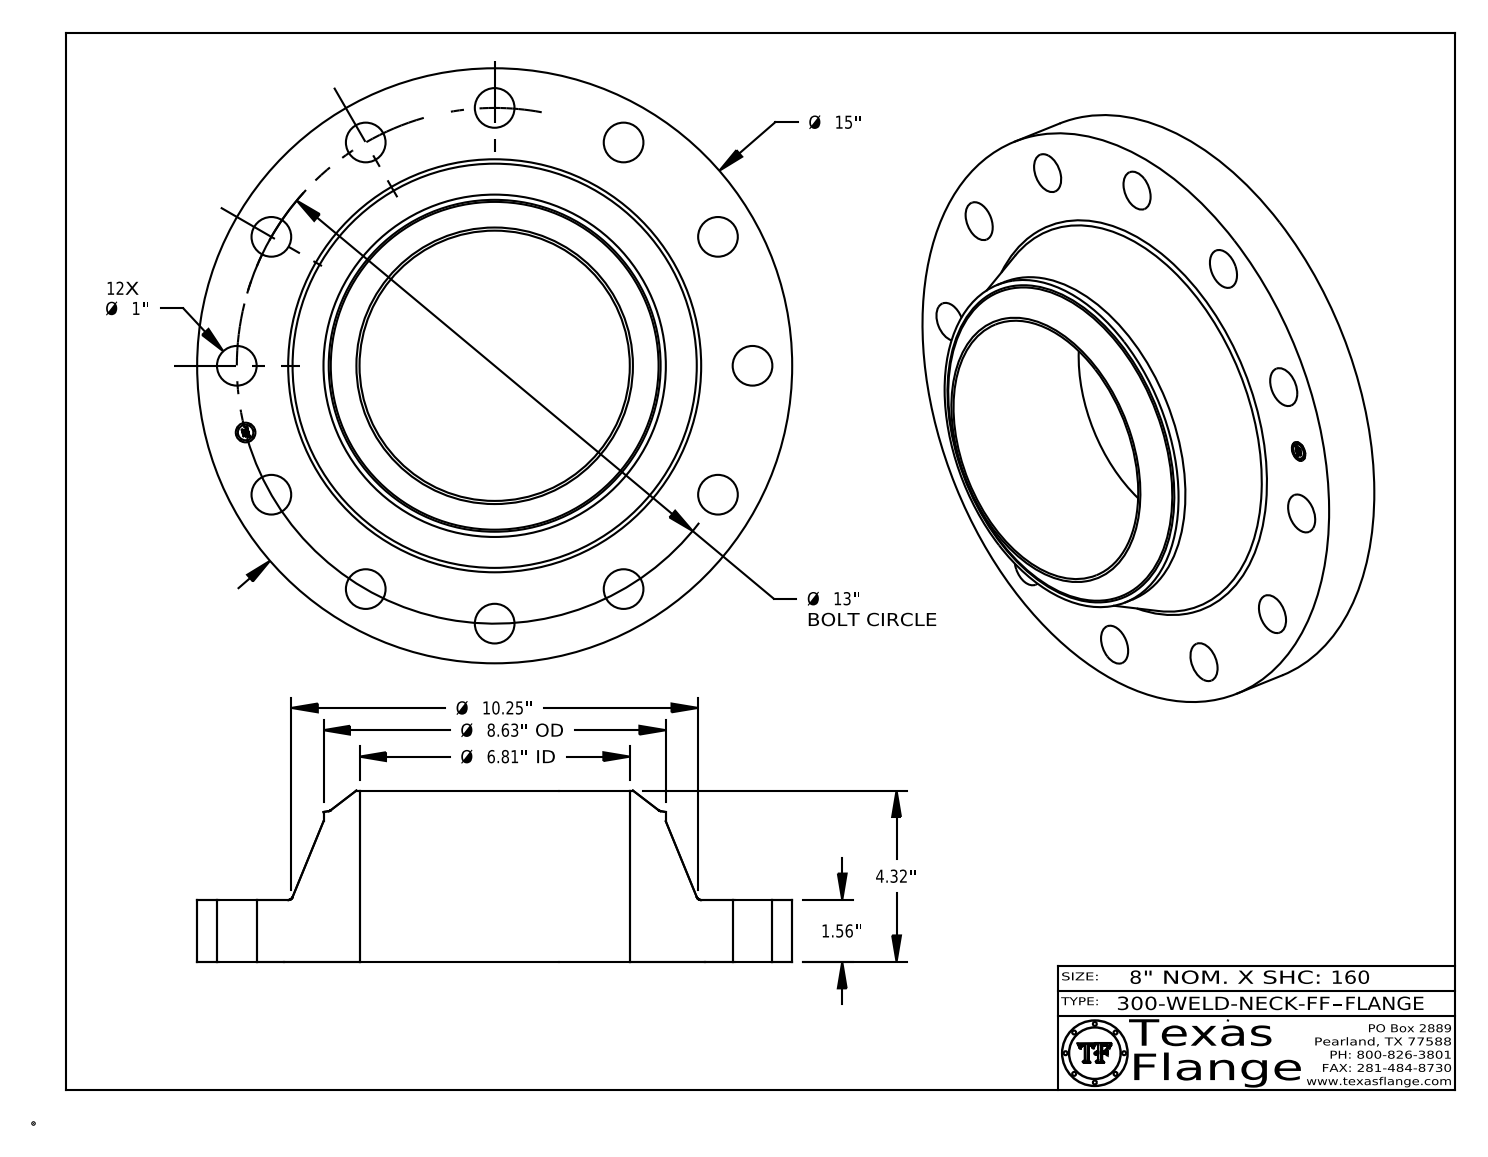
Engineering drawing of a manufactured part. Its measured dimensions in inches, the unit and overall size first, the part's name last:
Units: inches
Overall size (bounding box): 15 × 15 × 4.32
Round holes (diameter × count): ⌀1 ×12, ⌀0.495 ×1, ⌀6.813 ×1
Round bosses / shafts (diameter × count): ⌀0.03 ×8, ⌀15 ×1, ⌀8.63 ×1, ⌀0.39 ×1
Main face-to-face distances: 1.56, 4.32, 2.76, 1.545, 0.015, 2.775, 0.148, 0.144, 0.027, 0.096
Hole centre spacings: 6.5, 3.365, 9.193, 11.258, 12.557, 13, 1.697, 4.975
Volume: 281.6 in³ · Surface area: 536 in²
Bodies: 1 solid, 429 faces (369 planar, 50 cylindrical, 10 other)
Part name (STEP PRODUCT): 300-WELD-NECK-FF
STEP written by: CATIA V5 STEP AP214 (AUTOMOTIVE_DESIGN)
